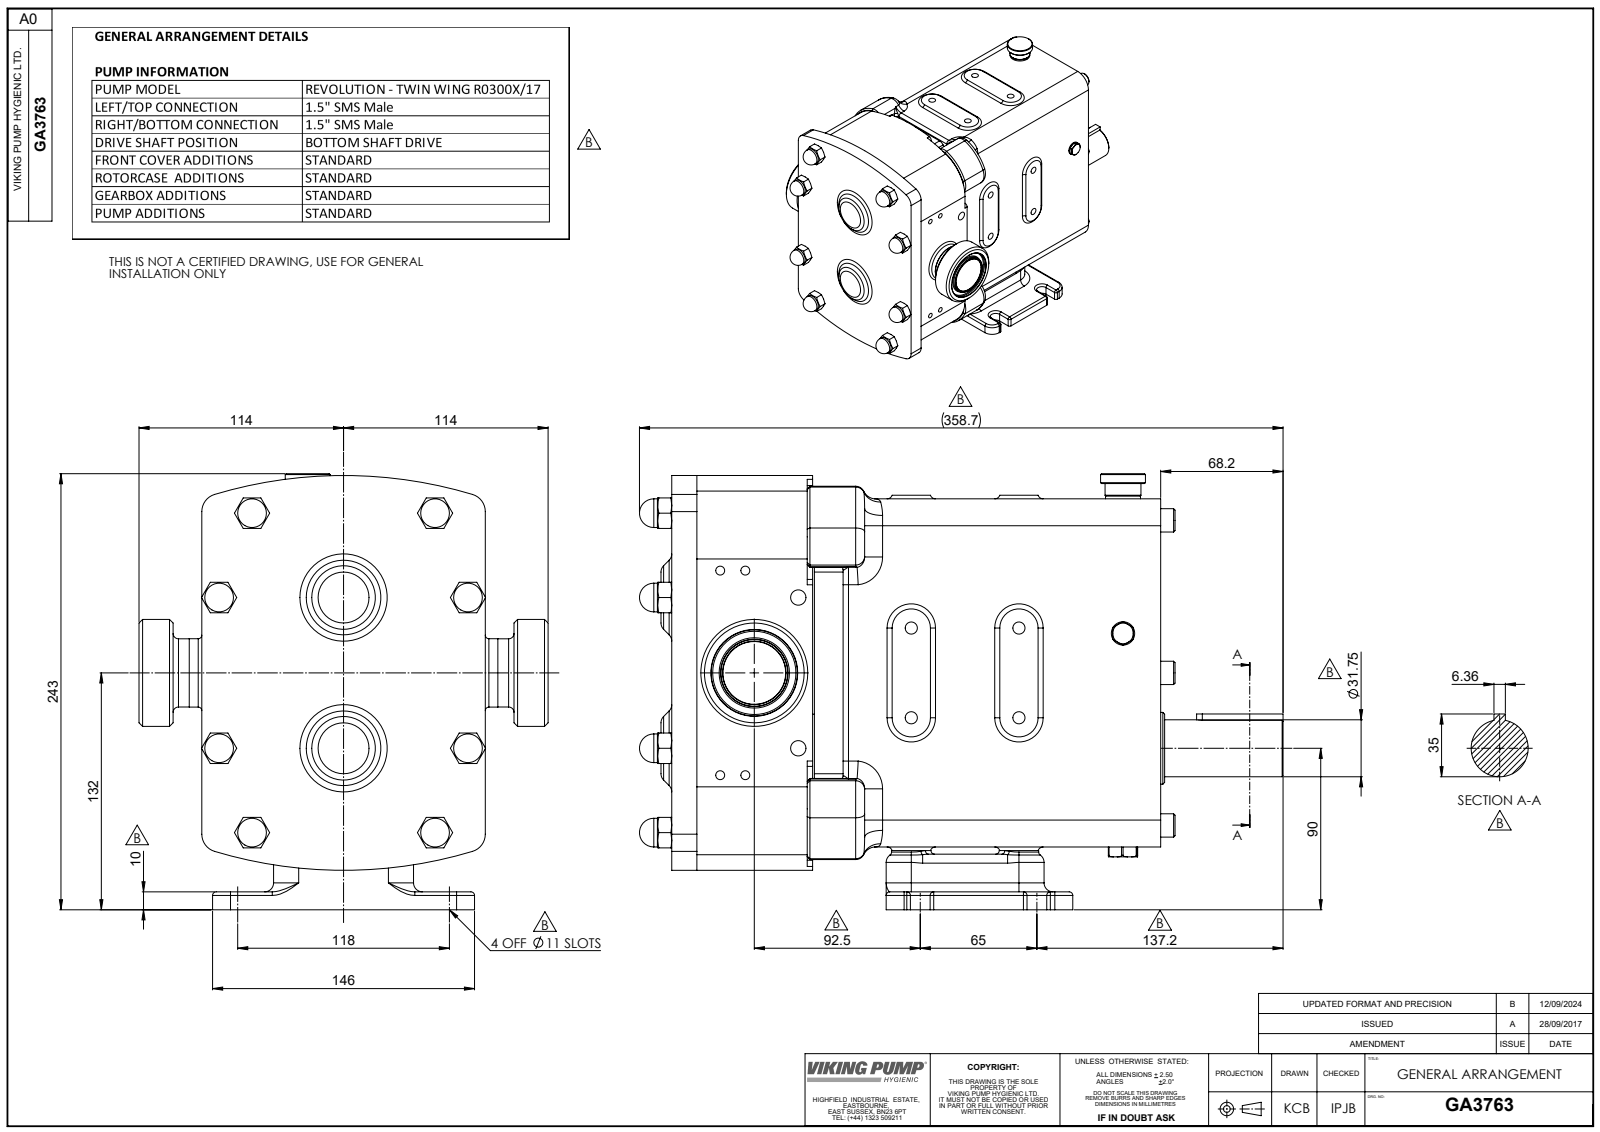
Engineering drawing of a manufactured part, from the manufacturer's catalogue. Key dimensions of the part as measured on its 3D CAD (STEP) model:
Part name (STEP PRODUCT): Copy of R0300 CPP H BSD^GA3763; GA3763; Copy of Z94-5101-22 - 1.5 INCH SMS681^GA3763
STEP written by: SolidWorks 2023 (AUTOMOTIVE_DESIGN)
Units: millimetres
Bodies: 3 solids, 971 faces (297 planar, 305 cylindrical, 369 other)
Overall size (bounding box): 358.7 × 243 × 228
Volume: 7 044 000 mm³ · Surface area: 374 187 mm²
Round holes (diameter × count): ⌀6.8 ×8, ⌀5 ×4, ⌀8.57 ×2, ⌀23 ×1, ⌀35 ×1, ⌀48 ×1
Round bosses / shafts (diameter × count): ⌀16 ×8, ⌀13 ×7, ⌀38 ×2, ⌀59.6 ×1, ⌀40 ×1, ⌀38.1 ×1, ⌀37.6 ×1, ⌀31.75 ×1
Partial cylindrical surfaces — rounded edges, fillets, slot ends (radius × count): R10 ×30, R3 ×28, R2 ×24, R5 ×19, R5.9 ×8, R15 ×8, R5.5 ×4, R8 ×4
Main face-to-face distances: 194, 24, 110, 78.5, 134, 272.5, 193, 79.5, 1, 22
Hole centre spacings: 50, 60, 78.1, 14, 33.11, 46.03, 48.63, 57.22
